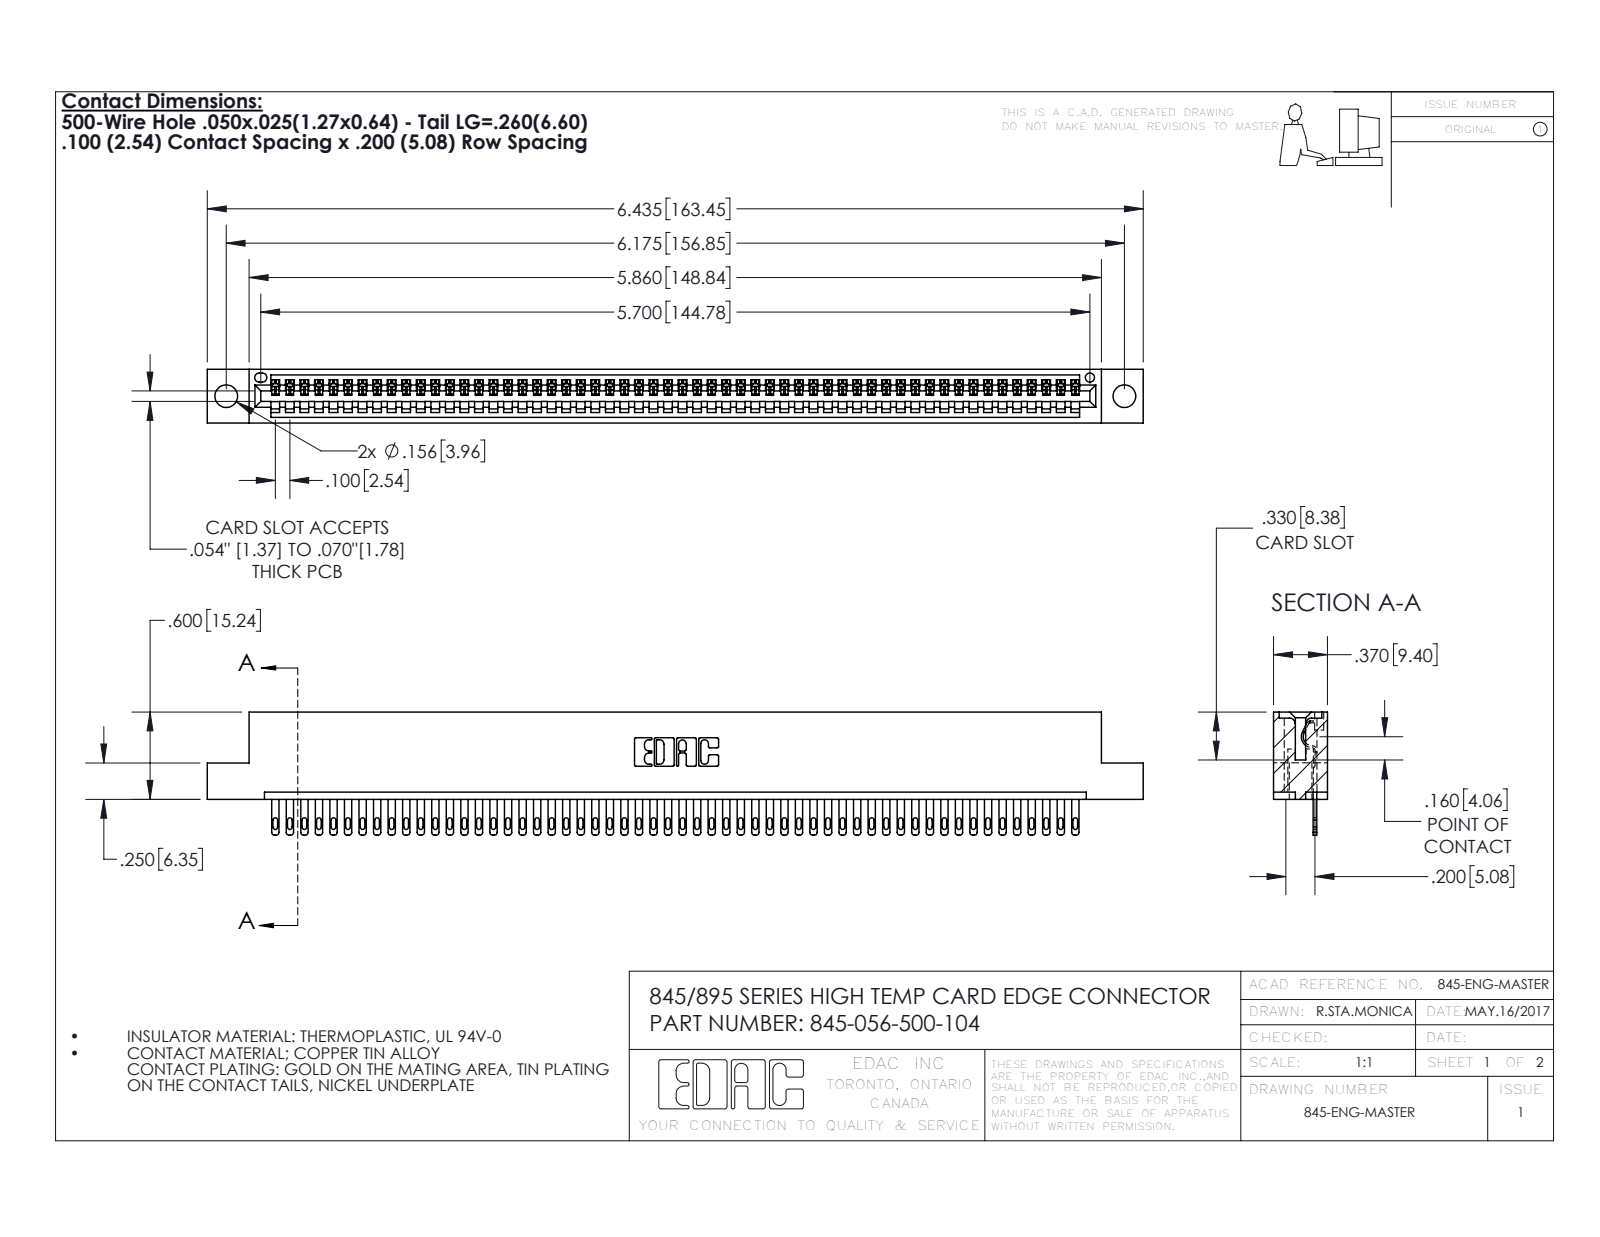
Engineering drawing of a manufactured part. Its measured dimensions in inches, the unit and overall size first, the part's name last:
Units: inches
Overall size (bounding box): 6.435 × 0.847 × 0.37
Round holes (diameter × count): ⌀0.156 ×2, ⌀0.064 ×1
Partial cylindrical surfaces — rounded edges, fillets, slot ends (radius × count): R0.006 ×112, R0.016 ×112, R0.02 ×112, R0.01 ×22, R0.007 ×6, R0.031 ×6, R0.026 ×3, R0.031 ×2
Main face-to-face distances: 0.298, 0.072, 0.37, 0.098, 0.272, 0.025, 0.2, 0.225, 0.149, 0.072
Hole centre spacings: 0.27, 5.939, 6.175
Volume: 0.951 in³ · Surface area: 32.3 in²
Bodies: 57 solids, 3150 faces (1984 planar, 1166 cylindrical, 0 other)
Part name (STEP PRODUCT): 345 Part_Flush Mounting Lugs - 0.156 Dia-TH; 345-292-001_345-293-100; 345-056-500-104
STEP written by: SolidWorks 2016 (CONFIG_CONTROL_DESIGN)
